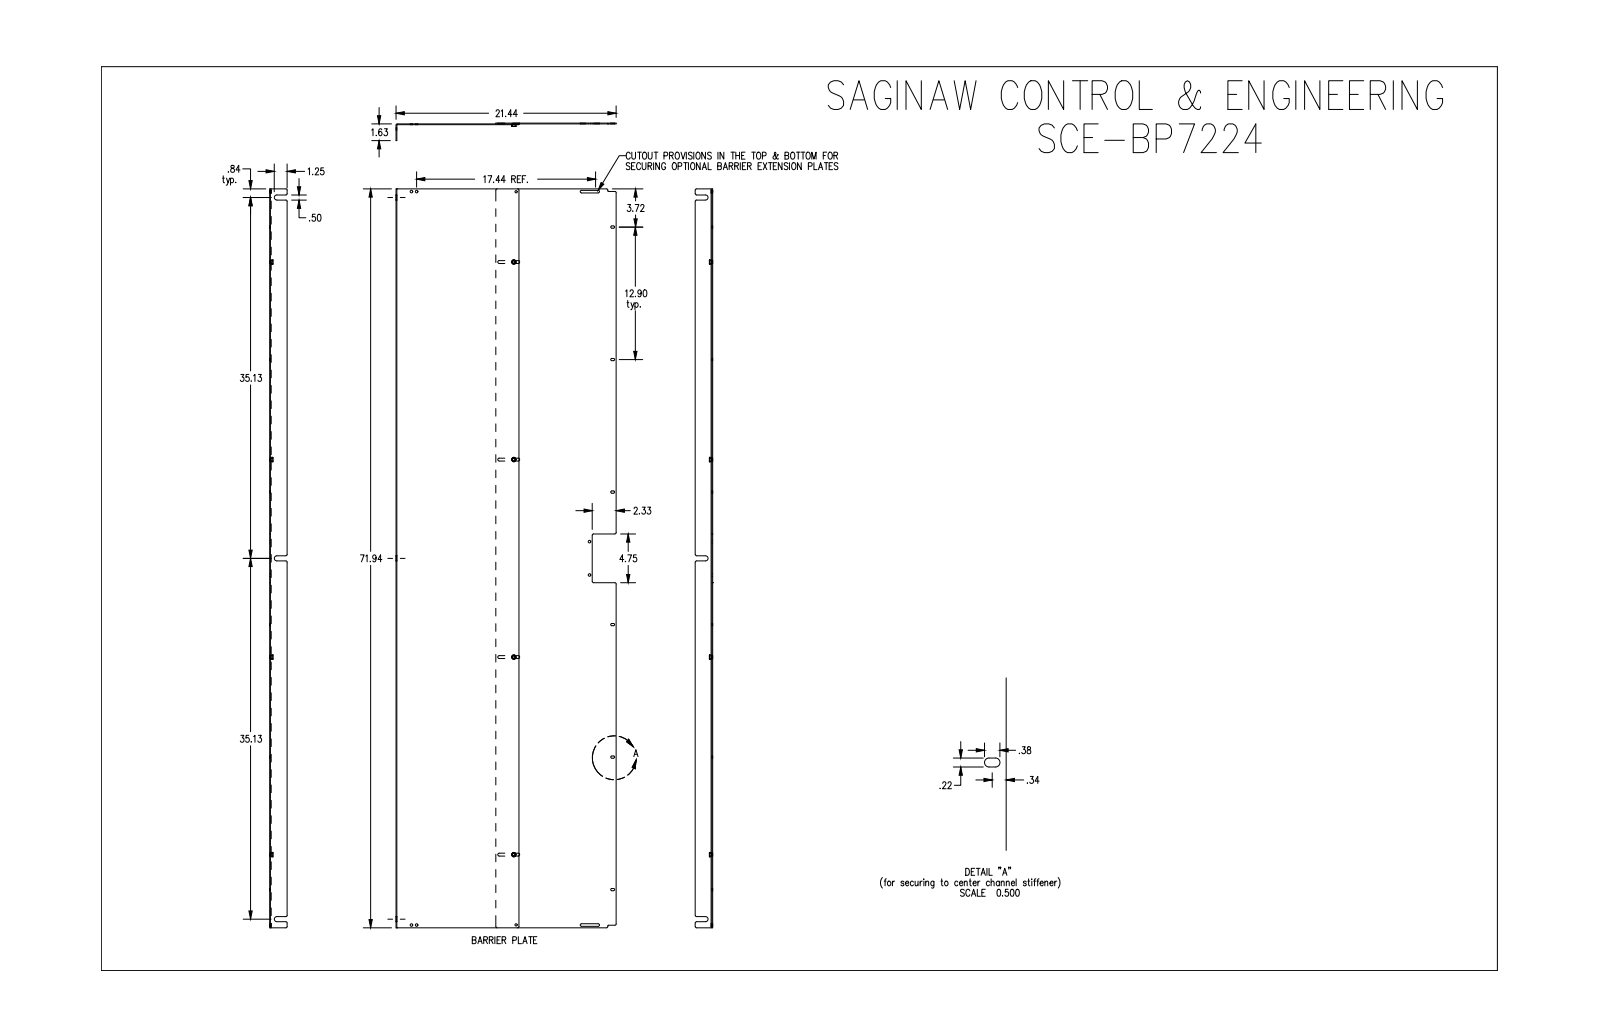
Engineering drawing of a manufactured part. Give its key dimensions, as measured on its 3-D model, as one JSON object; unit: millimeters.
{"part_name": "SCE-BP7224", "step_written_by": "SolidWorks 2019 (CONFIG_CONTROL_DESIGN)", "units": "millimeters", "bodies": {"solids": 6, "faces": 154, "planar": 67, "cylindrical": 75, "other": 12}, "overall_size": [1827.2, 544.6, 43.2], "volume_mm3": 2207000, "surface_area_mm2": 2337000, "round_holes": [[6.4, 10], [8.7, 4], [5.5, 2]], "round_bosses_or_shafts": [[11.2, 4], [8.7, 4]], "partial_cylinders_radius": [[3.2, 24], [2.8, 12], [3.6, 8], [6.4, 3], [1.6, 2], [1.1, 1], [3, 1]], "face_to_face_distances": [1.9, 3.8, 246.9, 245, 304, 302.1, 57.2, 43.2, 41.3, 39.4], "hole_center_spacings": [488.4, 12.7, 173.9, 246.1, 258.8, 276.1, 297, 307.3]}
